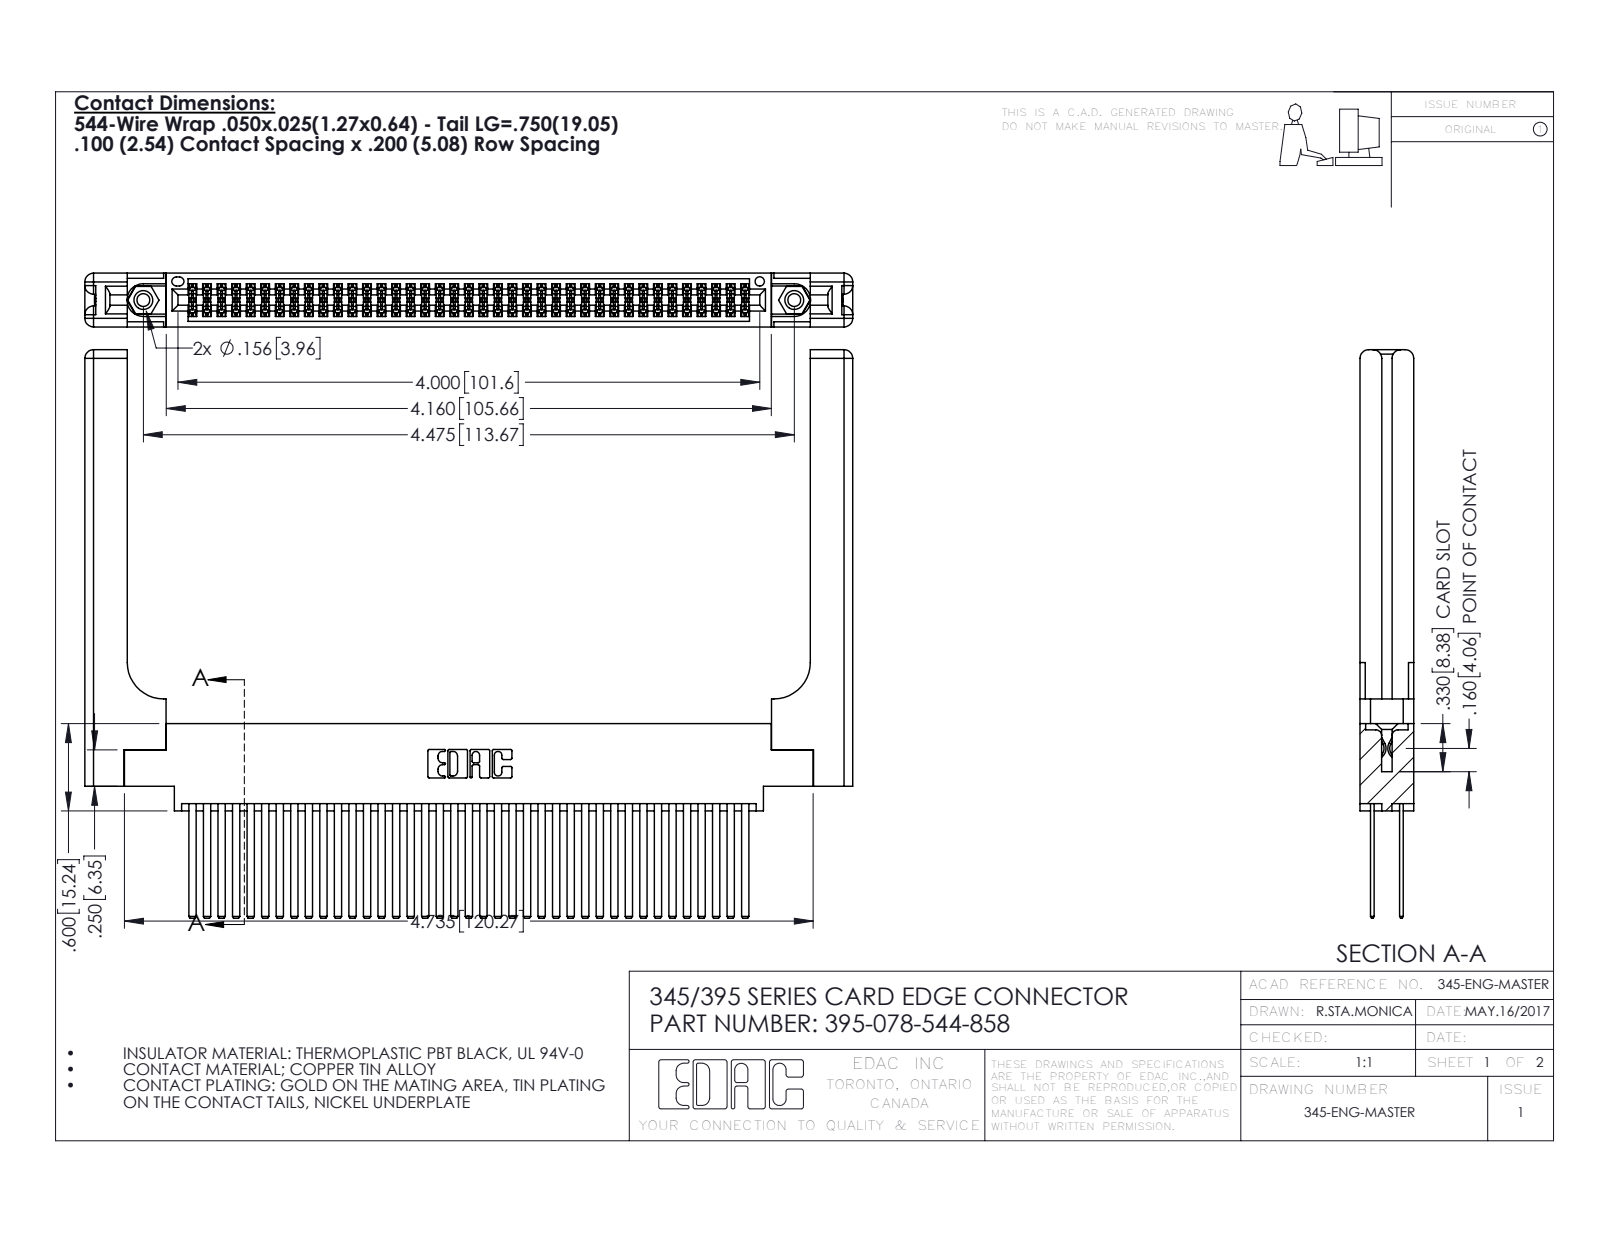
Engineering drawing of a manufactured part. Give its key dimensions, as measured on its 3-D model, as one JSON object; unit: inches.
{"part_name": "345-292-001_345-293-144; 345-250-001_345-250-001-102; 345 Part_0.170 Offset - 0.156 Dia-TH; 345-220-058_345-220-058 (+1 more)", "step_written_by": "SolidWorks 2016 (CONFIG_CONTROL_DESIGN)", "units": "inches", "bodies": {"solids": 83, "faces": 3818, "planar": 2494, "cylindrical": 1264, "other": 60}, "overall_size": [5.279, 3.907, 0.37], "volume_in3": 1.37, "surface_area_in2": 44.97, "round_holes": [[0.089, 2], [0.125, 2], [0.156, 2], [0.064, 1]], "round_bosses_or_shafts": [[0.155, 2]], "partial_cylinders_radius": [[0.006, 117], [0.01, 22], [0.06, 16], [0.007, 6], [0.031, 6], [0.026, 3], [0.014, 2], [0.019, 2]], "face_to_face_distances": [0.072, 0.298, 0.098, 0.272, 0.025, 0.2, 0.37, 0.225, 0.175, 0.148], "hole_center_spacings": [0.27, 4.239, 4.475]}
